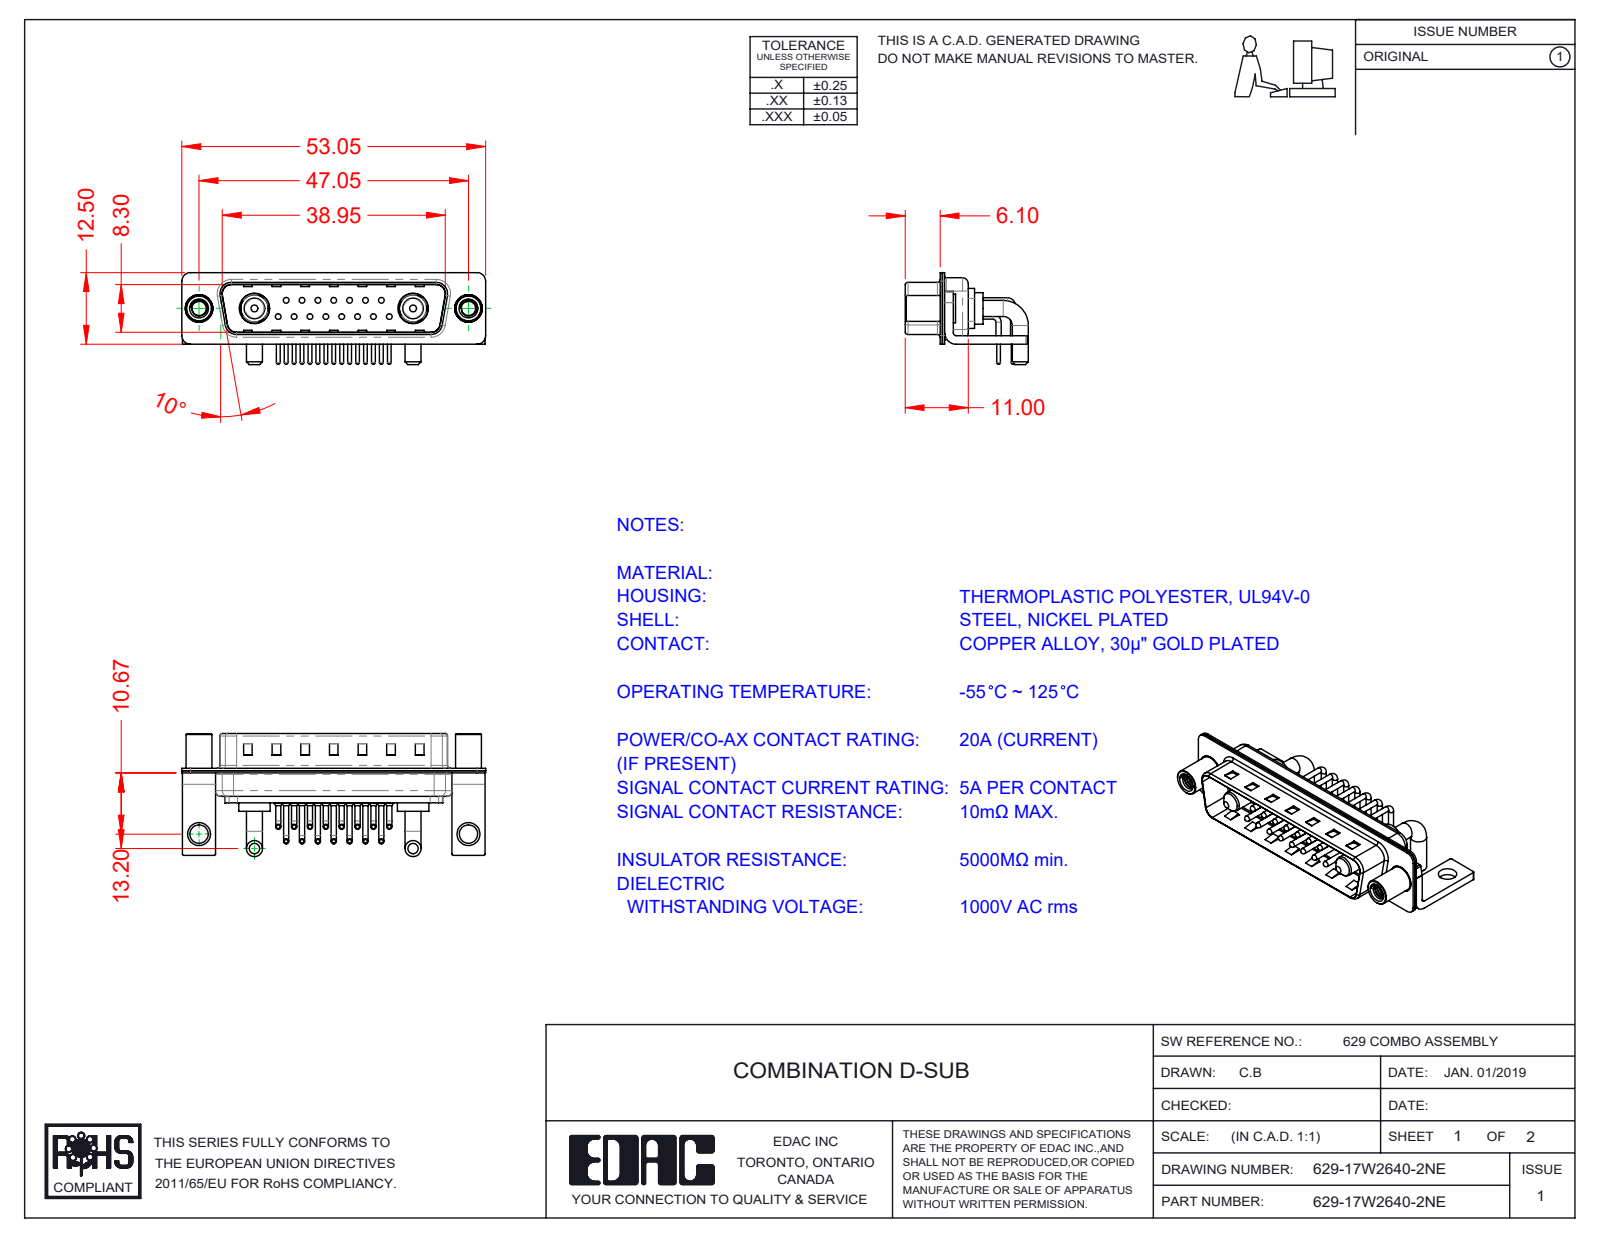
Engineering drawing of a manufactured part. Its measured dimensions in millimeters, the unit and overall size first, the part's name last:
Units: millimetres
Overall size (bounding box): 53.05 × 21.5 × 16.05
Round holes (diameter × count): ⌀0.75 ×15, ⌀1.6 ×15, ⌀2 ×15, ⌀2.5 ×2, ⌀3.2 ×2, ⌀4 ×2, ⌀4.8 ×2, ⌀4.85 ×2, ⌀5.3 ×2
Round bosses / shafts (diameter × count): ⌀0.9 ×30, ⌀1.5 ×15, ⌀1 ×15, ⌀0.65 ×15, ⌀2.8 ×4, ⌀5.5 ×2, ⌀5.2 ×2, ⌀5 ×2
Partial cylindrical surfaces — rounded edges, fillets, slot ends (radius × count): R0.25 ×16, R1.5 ×16, R1.01 ×15, R2 ×13, R0.5 ×9, R1.6 ×8, R0.6 ×4, R0.65 ×4
Main face-to-face distances: 0.4, 0.8, 9.5, 1.5, 9.1, 8.7, 9.9, 0.6, 5.2, 5.6
Hole centre spacings: 3.16, 2.77, 5.54, 8.31, 5.04, 7.49, 11.08, 5.03
Volume: 3 496 mm³ · Surface area: 8 400 mm²
Bodies: 26 solids, 2210 faces (1173 planar, 791 cylindrical, 246 other)
Part name (STEP PRODUCT): 629Combo Shell Front_25 Contacts; 629Combo Threaded Standoff_D; Power Pin_20A RA; 629Combo Shell Rear_25 Contacts (+5 more)
STEP written by: SolidWorks 2020 (CONFIG_CONTROL_DESIGN)
